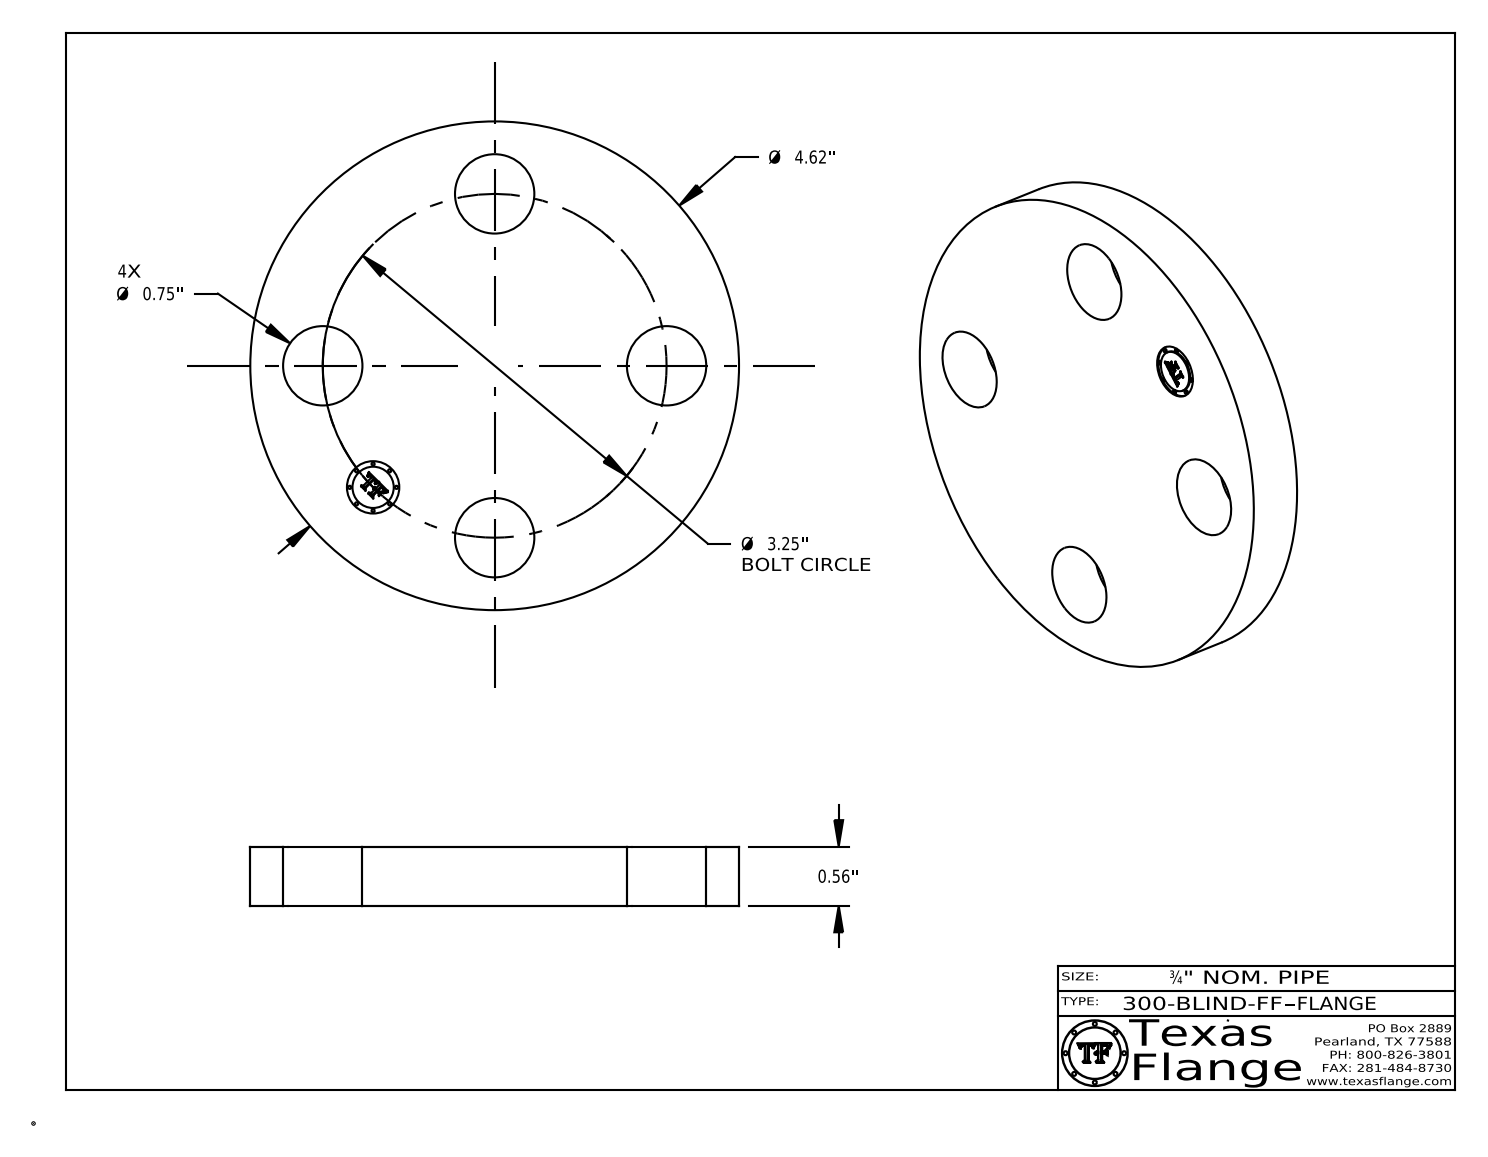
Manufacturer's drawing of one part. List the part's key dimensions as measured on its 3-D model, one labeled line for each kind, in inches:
Part name (STEP PRODUCT): 300-BLIND-FF
STEP written by: CATIA V5 STEP AP214 (AUTOMOTIVE_DESIGN)
Units: inches
Bodies: 1 solid, 397 faces (367 planar, 30 cylindrical, 0 other)
Overall size (bounding box): 4.62 × 4.62 × 0.56
Volume: 8.397 in³ · Surface area: 43.49 in²
Round holes (diameter × count): ⌀0.75 ×4, ⌀0.495 ×1
Round bosses / shafts (diameter × count): ⌀0.03 ×8, ⌀4.62 ×1, ⌀0.39 ×1
Main face-to-face distances: 0.56, 0.545, 0.015, 0.148, 0.144, 0.027, 0.096, 0.122, 0.021, 0.074
Hole centre spacings: 2.298, 1.244, 3.003, 3.25
